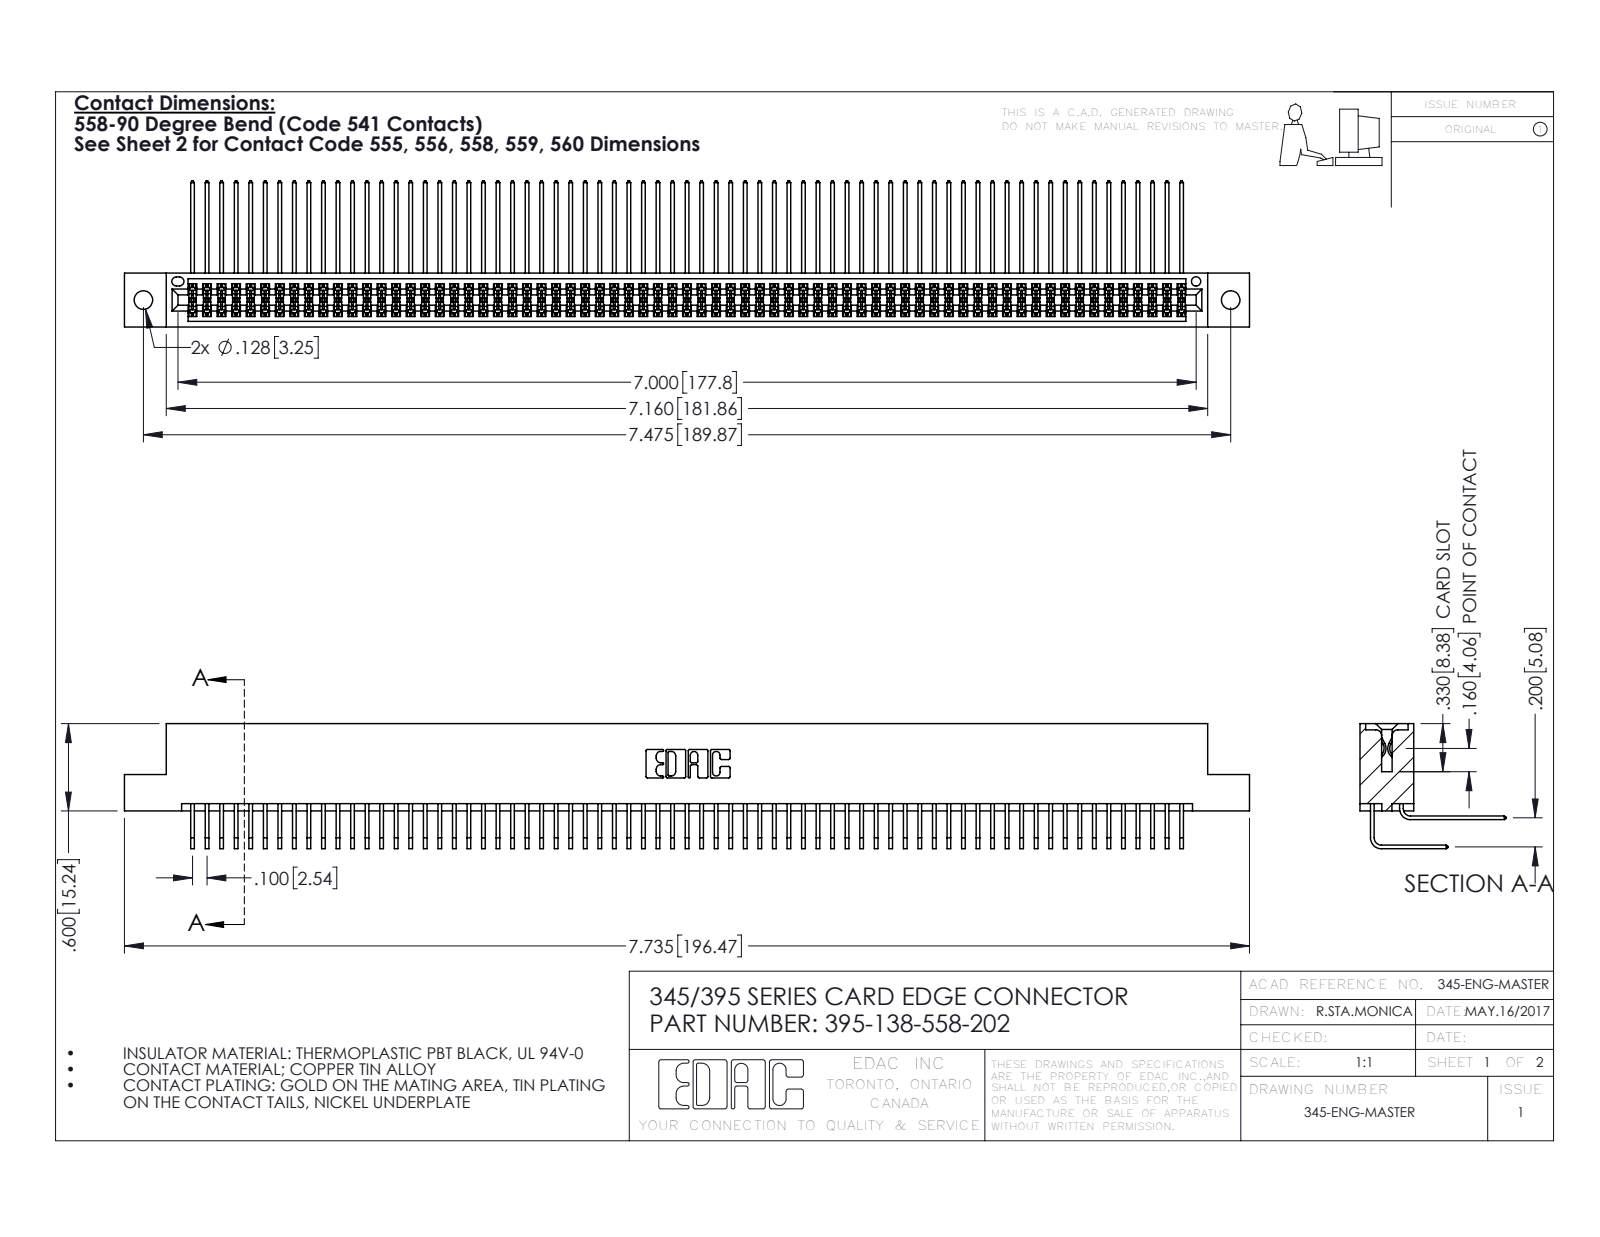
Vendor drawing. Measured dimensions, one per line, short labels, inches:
name: 395-138-558-202; 345-292-001_558 559 Tail - 1; 345 Part_Flush Mounting Lugs - 0.128 Dia; 345-292-001_558 Tail - 2
written by: SolidWorks 2016 (CONFIG_CONTROL_DESIGN)
unit: in
bodies: 139 solids, 7302 faces (4910 planar, 2392 cylindrical, 0 other)
size: 7.735 × 1.005 × 0.859
volume: 1.226 in³; area: 52.23 in²
holes: 2× ⌀0.128, 1× ⌀0.064
rounds: 275× R0.006, 22× R0.01, 6× R0.007, 6× R0.031, 3× R0.026, 2× R0.014, 2× R0.019, 2× R0.022
face distances: 0.072, 0.298, 0.2, 0.37, 0.098, 0.272, 0.025, 0.225, 0.025, 0.175
hole spacings: 0.27, 7.239, 7.475
